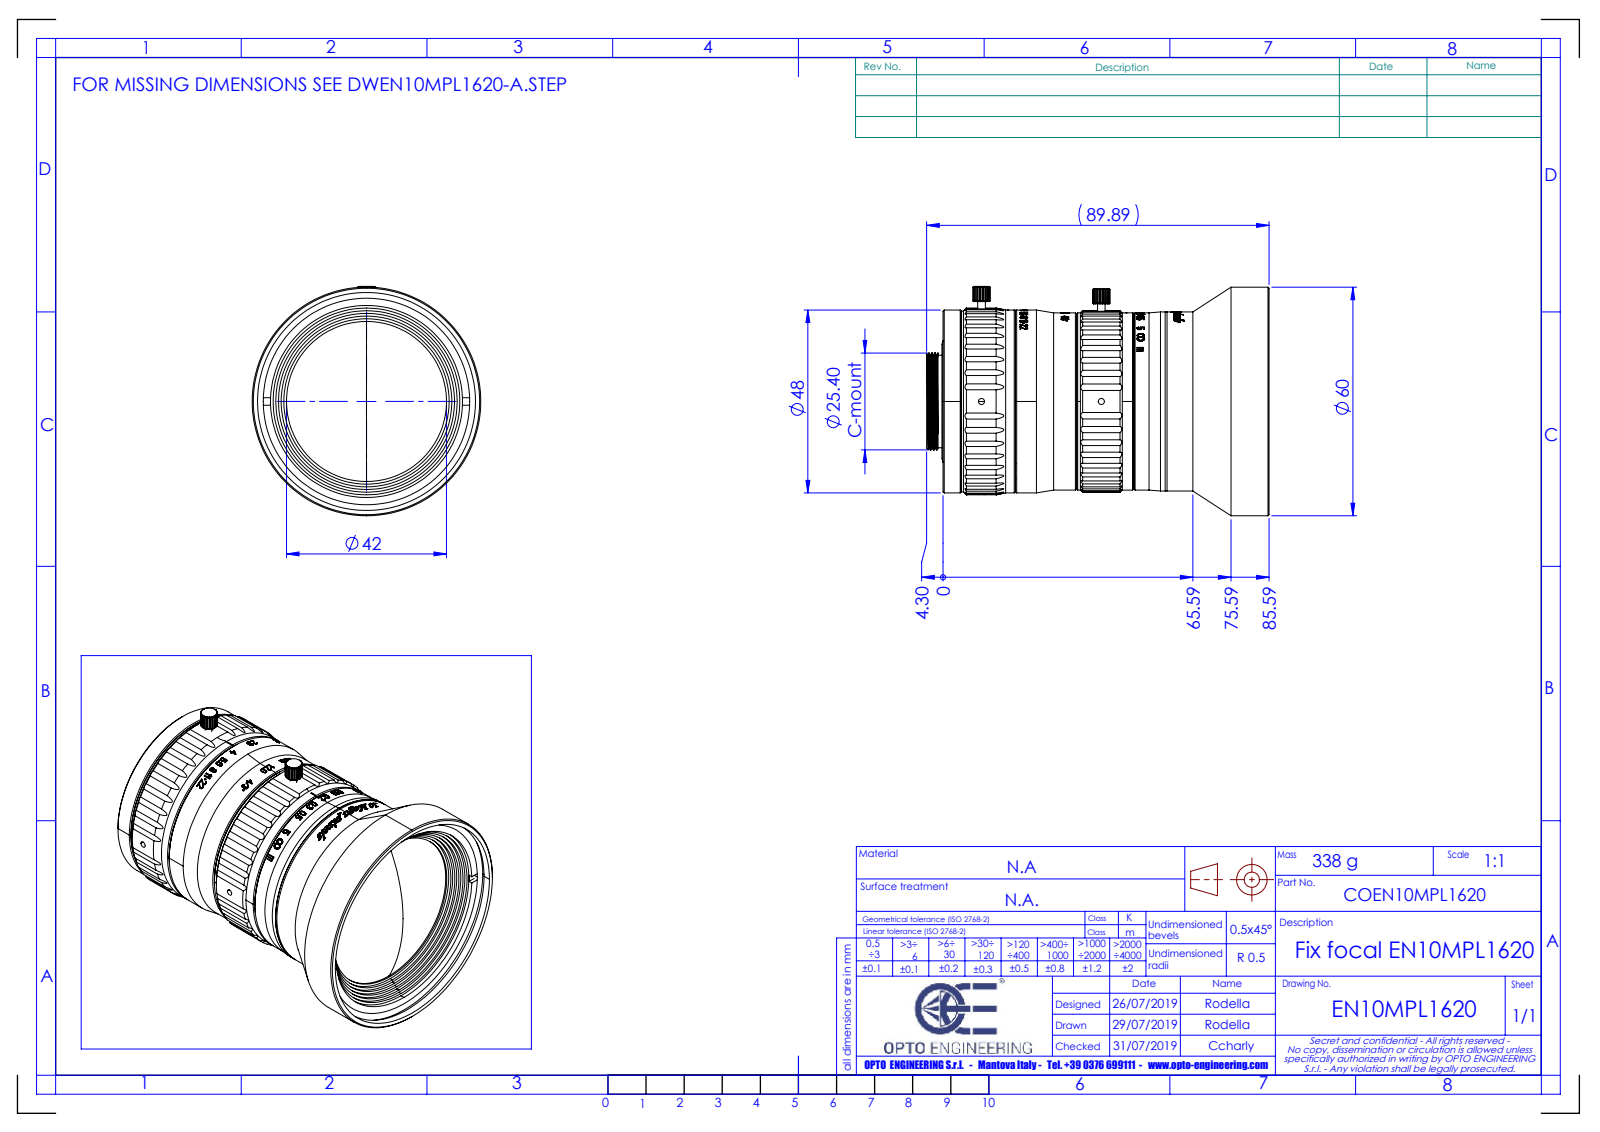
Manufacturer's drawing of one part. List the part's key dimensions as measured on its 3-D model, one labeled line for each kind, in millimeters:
Part name (STEP PRODUCT): FAL0011-0D-101; FAL0011-0D-102; FAL0011-0D-103; FAL0007-0D-103 (+8 more)
STEP written by: PRO/ENGINEER BY PARAMETRIC TECHNOLOGY CORPORATION, 2013230 (CONFIG_CONTROL_DESIGN)
Units: millimetres
Bodies: 13 solids, 2581 faces (653 planar, 555 cylindrical, 1373 other)
Overall size (bounding box): 89.89 × 60.2 × 60
Volume: 97 631 mm³ · Surface area: 83 136 mm²
Round holes (diameter × count): ⌀1.3 ×15, ⌀1.8 ×9, ⌀1.1 ×4, ⌀1.6 ×4, ⌀1.9 ×3, ⌀2.7 ×3, ⌀2.8 ×3, ⌀3 ×3, ⌀14 ×1, ⌀16.5 ×1, ⌀18 ×1, ⌀19 ×1
Round bosses / shafts (diameter × count): ⌀2 ×2, ⌀60 ×1, ⌀55 ×1, ⌀53 ×1, ⌀49 ×1, ⌀48 ×1, ⌀47.4 ×1, ⌀47 ×1
Partial cylindrical surfaces — rounded edges, fillets, slot ends (radius × count): R1 ×76, R1.25 ×12, R1.5 ×4, R2 ×4, R1.4 ×3, R2.25 ×2, R16 ×1, R18 ×1
Main face-to-face distances: 1.5, 27.01, 47.93, 73.44, 50.51, 23.5, 1.82, 75.26, 27.33, 25.51
Hole centre spacings: 19.49, 18.43, 21.46, 22.04, 26.88, 39.67, 3.75, 4.05
